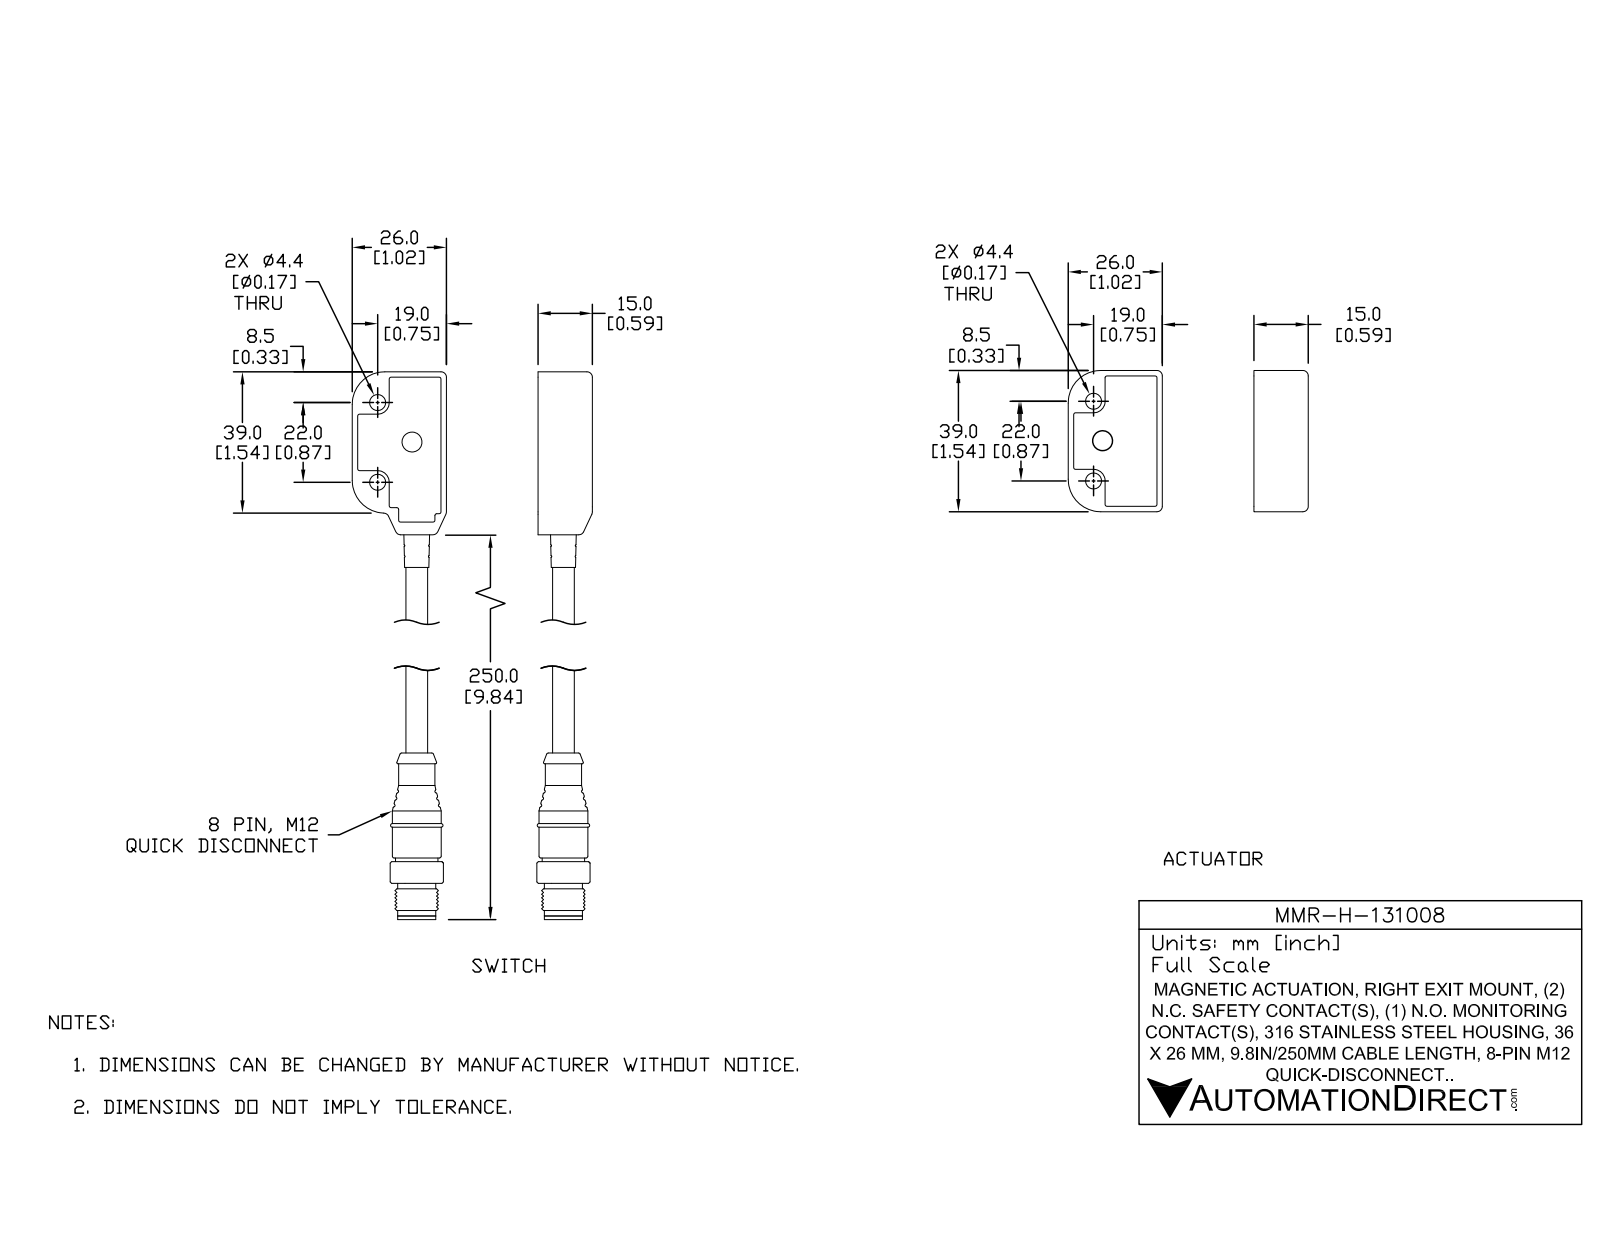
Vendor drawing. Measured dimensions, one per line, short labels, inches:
name: MMR-H-131008_2; MMR-H-131008_1; MMR-H-131008
written by: SolidWorks 2017 (AUTOMOTIVE_DESIGN)
unit: in
bodies: 8 solids, 943 faces (330 planar, 336 cylindrical, 277 other)
size: 11.614 × 2.087 × 0.604
volume: 1.614 in³; area: 37.65 in²
holes: 4× ⌀0.173, 2× ⌀0.197, 1× ⌀0.232, 1× ⌀0.283, 1× ⌀0.327, 1× ⌀0.465
bosses: 8× ⌀0.031, 2× ⌀0.079, 1× ⌀0.531, 1× ⌀0.461, 1× ⌀0.413, 1× ⌀0.394, 1× ⌀0.374, 1× ⌀0.339
rounds: 82× R0.02, 26× R0.012, 15× R0.059, 8× R0.008, 6× R0.157, 4× R0.126, 4× R0.13, 4× R0.181
face distances: 0.059, 0.575, 0.516, 0.461, 0.098, 0.52, 0.055, 0.591, 0.531, 0.965
hole spacings: 0.866, 1.535, 1.763, 0.44, 0.448, 0.569, 0.575, 1.063
